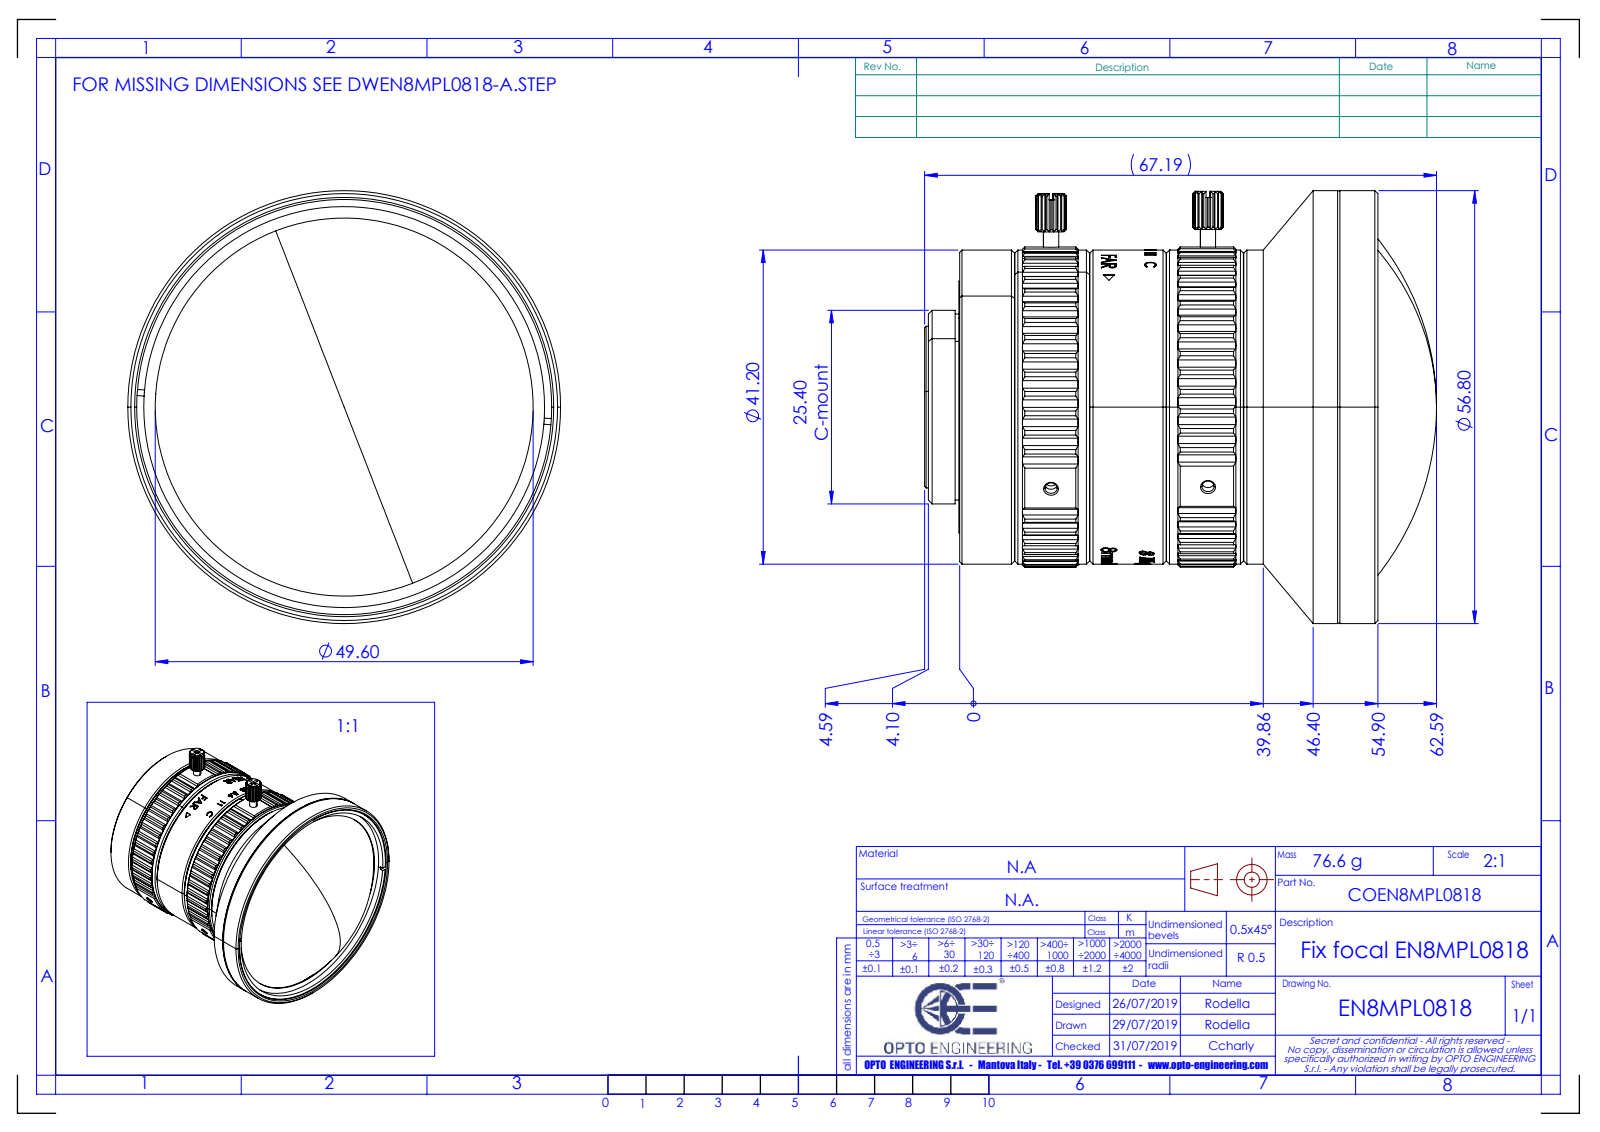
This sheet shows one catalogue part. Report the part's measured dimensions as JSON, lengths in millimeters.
{"part_name": "EN8MPL0818-02; EN8MPL0818-03; EN8MPL0818-04; EN8MPL0818-05 (+8 more)", "step_written_by": "PRO/ENGINEER BY PARAMETRIC TECHNOLOGY CORPORATION, 2015240 (CONFIG_CONTROL_DESIGN)", "units": "millimeters", "bodies": {"solids": 18, "faces": 1874, "planar": 730, "cylindrical": 315, "other": 829}, "overall_size": [67.19, 56.8, 56.8], "volume_mm3": 18099, "surface_area_mm2": 28958, "round_holes": [[1.6, 6], [2.9, 4], [1, 2], [15.4, 1], [16.4, 1], [18.46, 1], [19, 1], [22, 1], [23.26, 1], [39.54, 1], [49.6, 1], [50.6, 1]], "round_bosses_or_shafts": [[2.8, 4], [2, 2], [56.8, 1], [56.7, 1], [53, 1], [41.2, 1], [25.4, 1], [24.4, 1]], "partial_cylinders_radius": [[2, 5], [0.5, 2], [1.9, 2], [20.1, 1], [20.5, 1], [21, 1]], "face_to_face_distances": [0.65, 3.5, 2.85, 0.75, 2.75, 51.49, 52.14, 52.24, 54.99, 0.6], "hole_center_spacings": [14.69, 20.78, 8.64, 9.4, 12.28, 21.4, 23.11, 29.39]}
